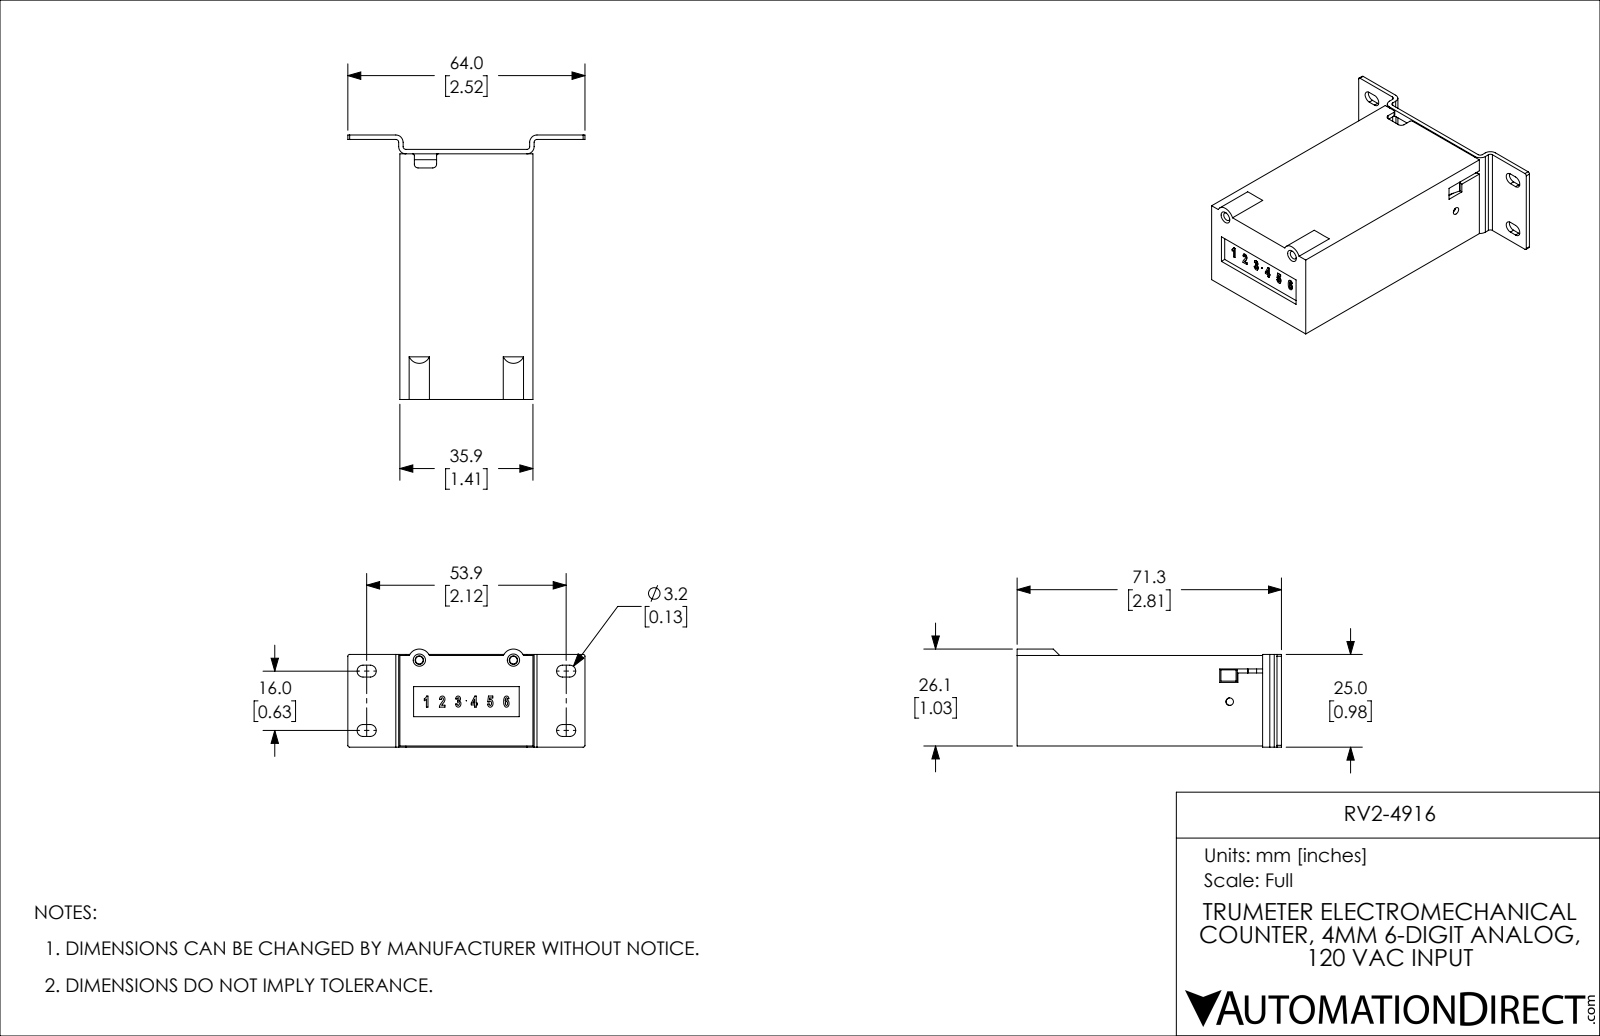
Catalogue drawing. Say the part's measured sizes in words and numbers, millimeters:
The part is named "RV2-4916". Its 3-D file was written by "SolidWorks 2021 (CONFIG_CONTROL_DESIGN)". It is 1 solid with 354 faces: 219 planar, 104 cylindrical and 31 other. Overall it measures 71.33 by 64 by 26.46 millimeters. Its volume is 18 281 cubic millimeters and its surface area 26 612 square millimeters. Round holes: 5 of diameter 2.02, 2 of diameter 3.17, 2 of diameter 4, 1 of diameter 2.01, 1 of diameter 2.03, 1 of diameter 2.46, 1 of diameter 2.46, 1 of diameter 3.12, 1 of diameter 5.6. Round bosses or shafts: 2 of diameter 6. Partial cylindrical surfaces (rounded edges, fillets, slot ends): 11 of radius 0.5, 10 of radius 1, 8 of radius 1.6, 4 of radius 0.75, 4 of radius 1.95, 2 of radius 0.25, 2 of radius 0.3, 2 of radius 1.5. The main face-to-face distances are 1.6, 1.35, 34.55, 2.95, 32.95, 31.6, 24.39, 35.9, 33.2, 30. The hole center spacings are 13.21, 25.86, 26.65, 26.67, 4.75, 5, 7.03, 8.14.
